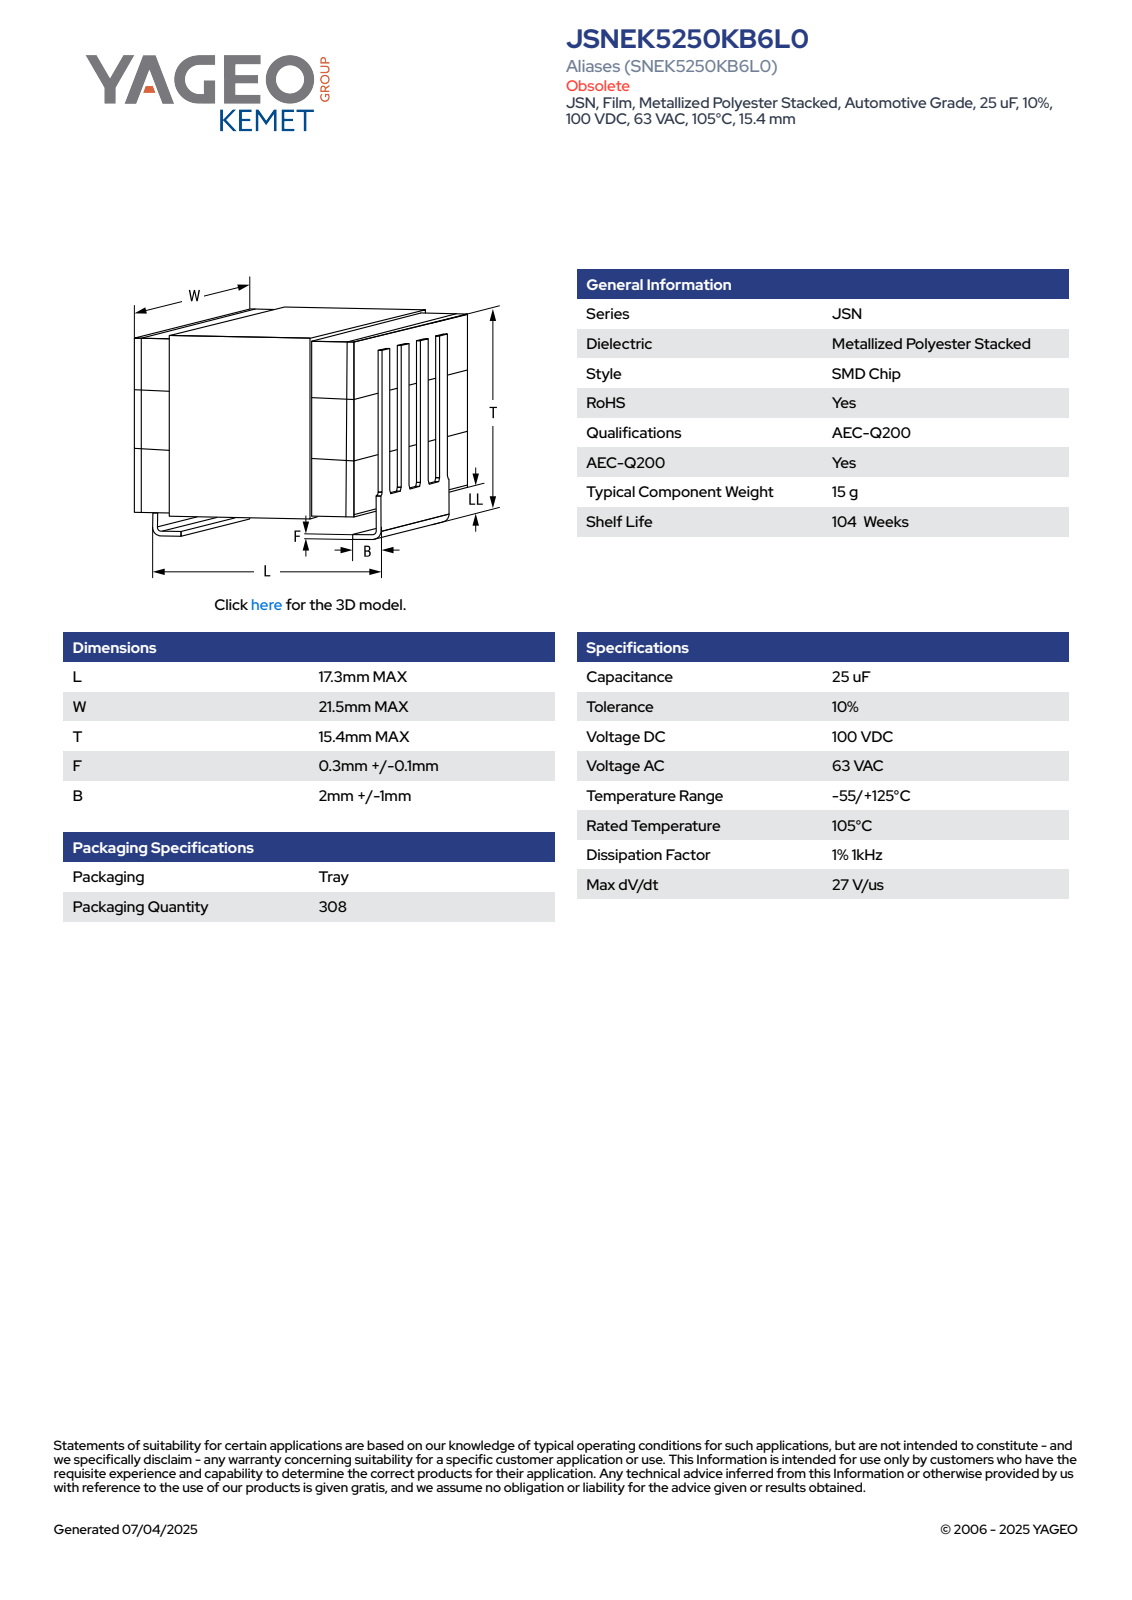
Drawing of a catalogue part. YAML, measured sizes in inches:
part_name: "CFS_KJSN_L17.3W21.5T15.4F0.40"
step_written_by: "SolidWorks 2014 (AUTOMOTIVE_DESIGN)"
units: inches
bodies: {solids: 4, faces: 101, planar: 97, cylindrical: 4, other: 0}
overall_size: [0.846, 0.681, 0.606]
volume: 0.273
surface_area: 4.493
partial_cylinders:
  - {radius: 0.008, count: 4}
face_to_face_distances: [0.161, 0.324, 0.32, 0.157, 0.163, 0.016, 0.665, 0.165, 0.328, 0.484]
